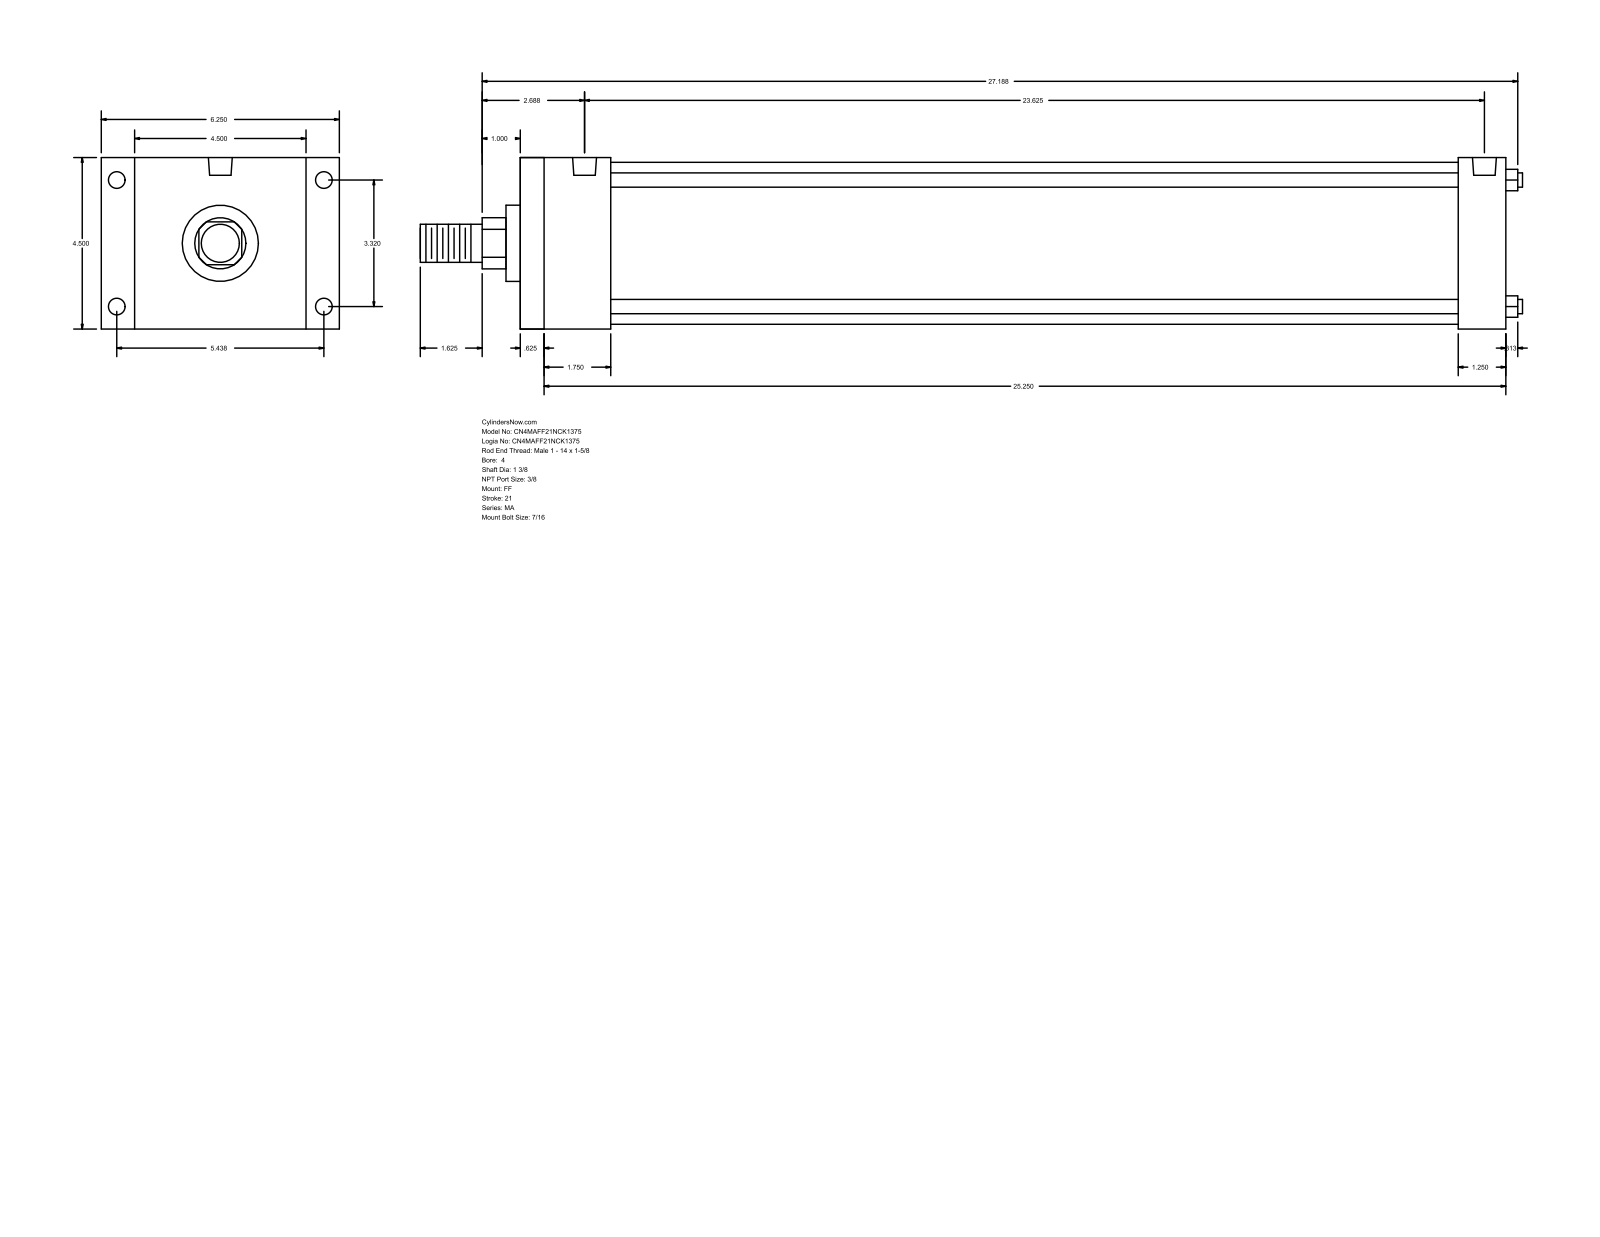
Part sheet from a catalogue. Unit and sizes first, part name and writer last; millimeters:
Units: millimetres
Overall size (bounding box): 735.01 × 158.75 × 114.3
Round holes (diameter × count): ⌀11.11 ×8, ⌀15.93 ×2
Round bosses / shafts (diameter × count): ⌀9.53 ×4, ⌀107.95 ×1, ⌀50.8 ×1, ⌀34.92 ×1, ⌀25.4 ×1
Partial cylindrical surfaces — rounded edges, fillets, slot ends (radius × count): R17.06 ×1
Main face-to-face distances: 114.3, 657.22, 15.87, 641.35, 22.23, 136.53, 625.48, 609.61, 31.74, 60.32
Hole centre spacings: 84.32, 138.12, 161.82, 590.55, 4.76, 4.77, 595.31, 595.32
Bodies: 0 solids, 92 faces (64 planar, 28 cylindrical, 0 other)
Part name (STEP PRODUCT): MA_FF__0400_1.375
STEP written by: GSSL Pune (CONFIG_CONTROL_DESIGN)
